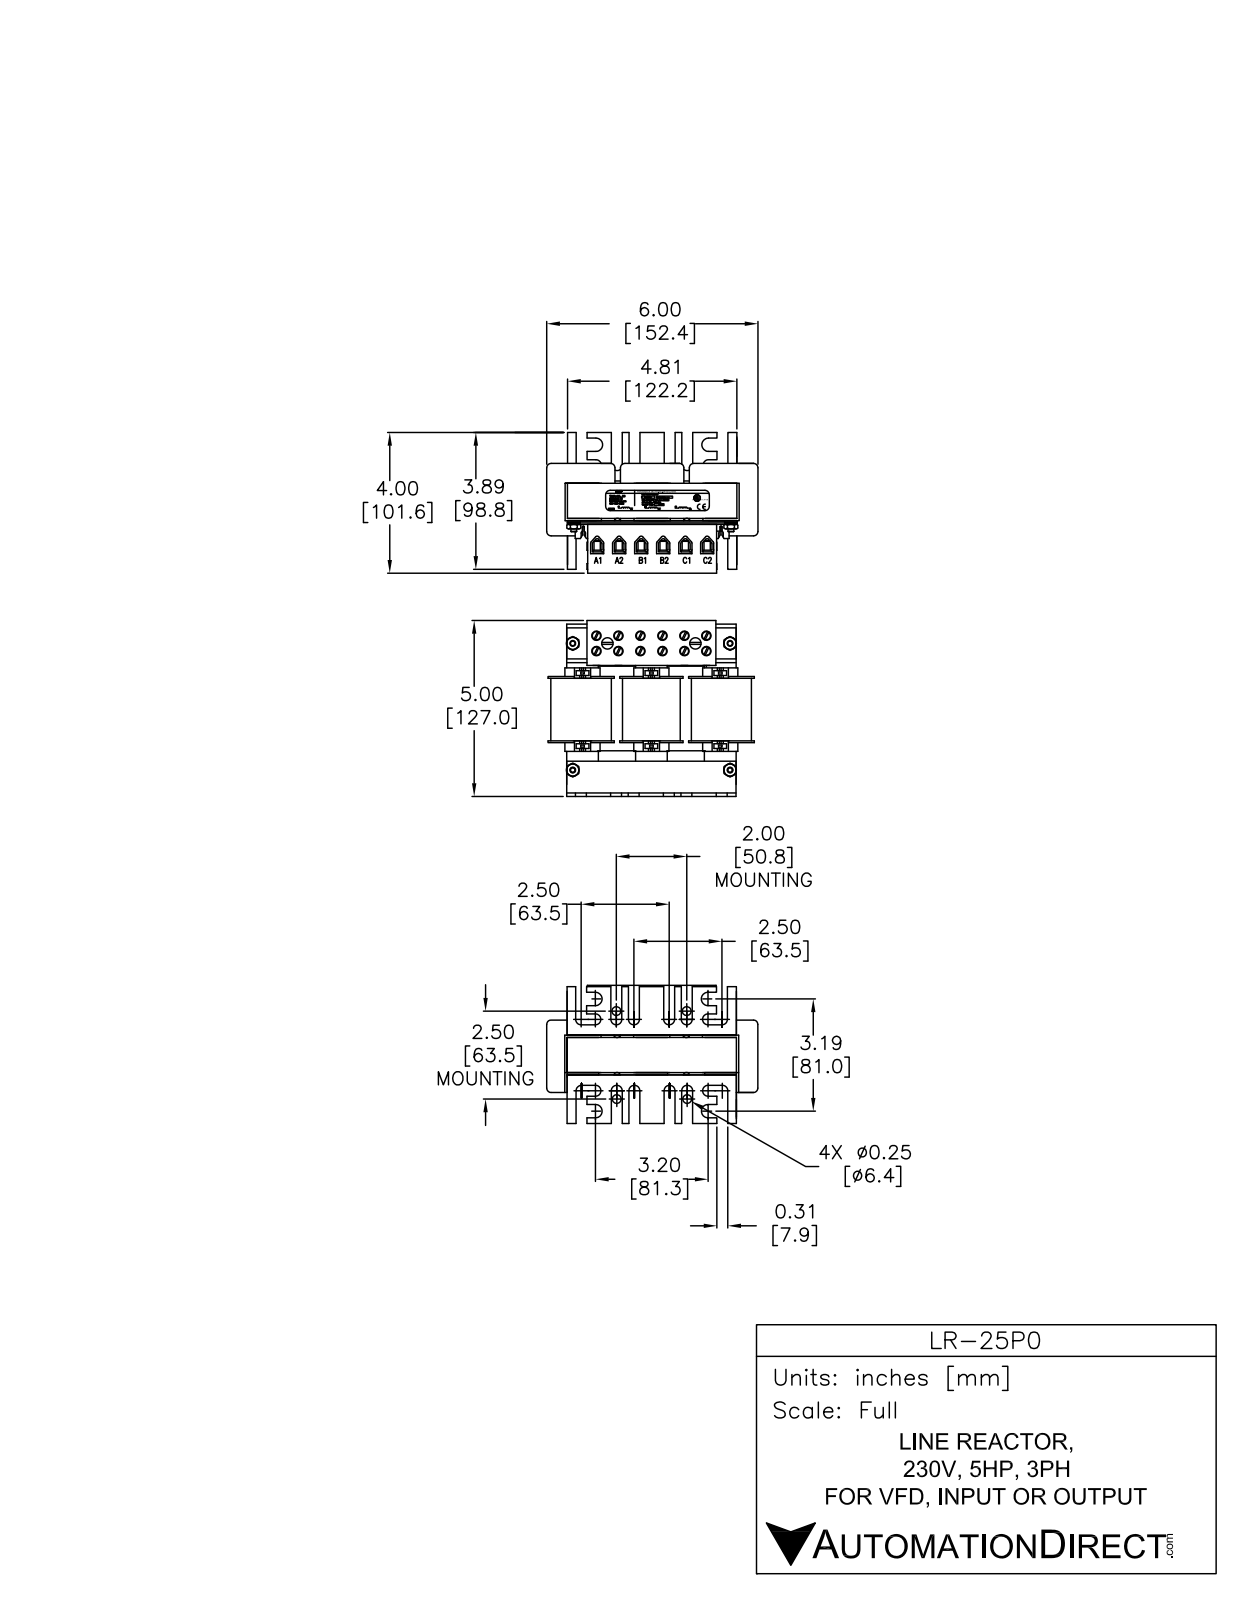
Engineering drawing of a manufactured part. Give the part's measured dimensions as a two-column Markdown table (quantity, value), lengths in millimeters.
| quantity | value |
| --- | --- |
| part name | LR-25P0 |
| STEP written by | SolidWorks 2011 (AUTOMOTIVE_DESIGN) |
| units | millimeters |
| bodies | 43 solids, 1048 faces (794 planar, 222 cylindrical, 32 other) |
| overall size | 144.75 × 131.2 × 98.38 |
| volume | 540 879 mm³ |
| surface area | 167 068 mm² |
| round holes (diameter × count) | 7 × 12, 7.75 × 5 |
| round bosses / shafts (diameter × count) | 7 × 12, 10.25 × 4, 8 × 4, 7.75 × 2, 7.5 × 2, 3.4 × 2, 3.25 × 2 |
| partial cylindrical surfaces (radius × count) | 3.94 × 16, 1.82 × 12, 2.68 × 12, 2.71 × 12, 5 × 12, 6 × 12, 4.83 × 4, 0.86 × 3 |
| main face-to-face distances | 2.5, 27.26, 1.5, 31.25, 5.62, 34.88, 28.76, 34.38, 7.12, 32.88 |
| hole center spacings | 16, 32, 21.26, 34.93, 48, 14, 50, 10.34 |
